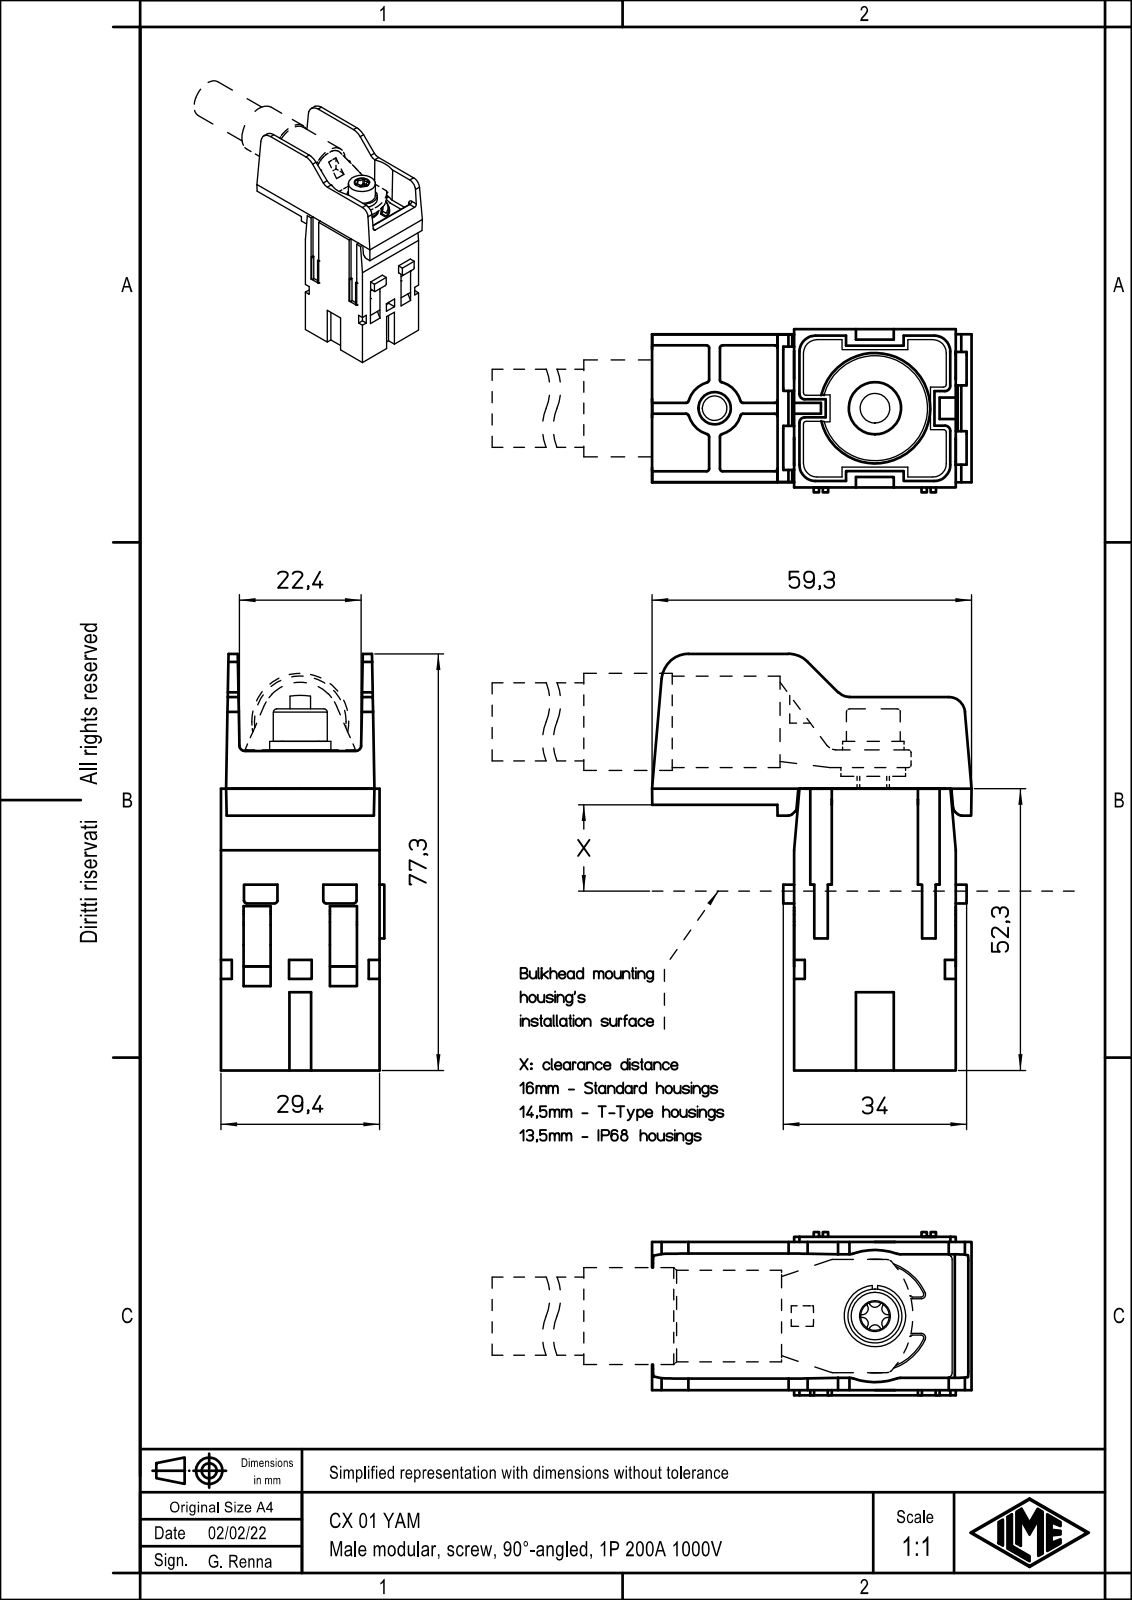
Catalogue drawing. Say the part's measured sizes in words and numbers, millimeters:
The part is named "CX 01 YAM". Its 3-D file was written by "Creo Elements/Direct Modeling 20.1B 02-Apr-2019 (C) Parametric Technology GmbH (AUTOMOTIVE_DESIGN)". It is 1 solid with 440 faces: 257 planar, 132 cylindrical and 51 other. Overall it measures 77.3 by 59.3 by 30.3 millimeters. Its volume is 48 255 cubic millimeters and its surface area 20 033 square millimeters. Round holes: 1 of diameter 6, 1 of diameter 19.5. Round bosses or shafts: 1 of diameter 12, 1 of diameter 11.4, 1 of diameter 10, 1 of diameter 9.5, 1 of diameter 6. Partial cylindrical surfaces (rounded edges, fillets, slot ends): 60 of radius 0.5, 6 of radius 0.26, 6 of radius 1.12, 4 of radius 1, 4 of radius 2.5, 3 of radius 5, 2 of radius 0.3, 2 of radius 3. The main face-to-face distances are 0.95, 28.45, 3.5, 25.9, 2.55, 24.95, 27.5, 30, 29.4, 22.4. The hole center spacings are 29.75.
